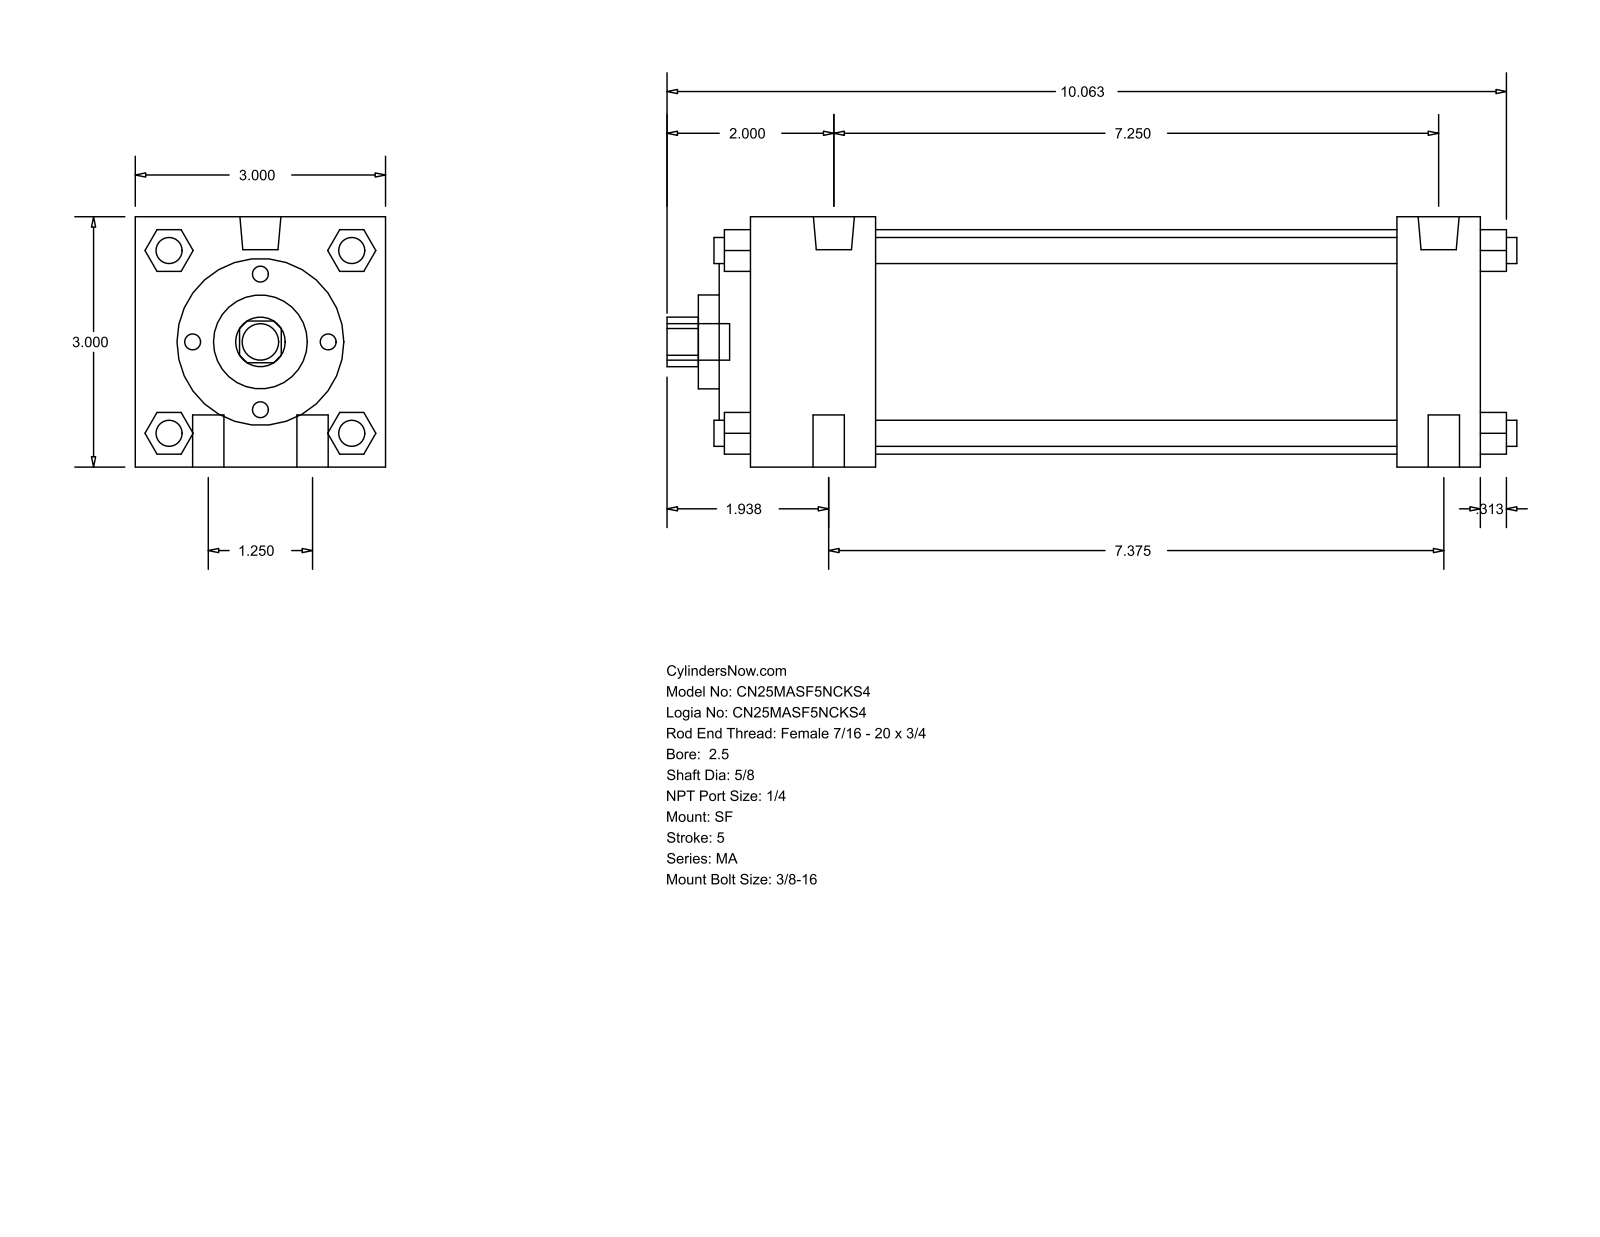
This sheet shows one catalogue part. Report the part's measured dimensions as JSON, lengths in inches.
{"part_name": "MA_SF__0250_0.625", "step_written_by": "GSSL Pune (CONFIG_CONTROL_DESIGN)", "units": "inches", "bodies": {"solids": 0, "faces": 126, "planar": 95, "cylindrical": 31, "other": 0}, "overall_size": [10.187, 3, 3], "round_holes": [[0.625, 1], [1.125, 1], [2, 1], [2.69, 1]], "round_bosses_or_shafts": [[0.313, 6], [0.375, 4], [0.492, 2], [0.437, 1]], "partial_cylinders_radius": [[0.297, 1]], "face_to_face_distances": [3, 8.75, 1, 7.75, 1.5, 6.25, 7.25, 0.5, 0.375, 1.875]}
